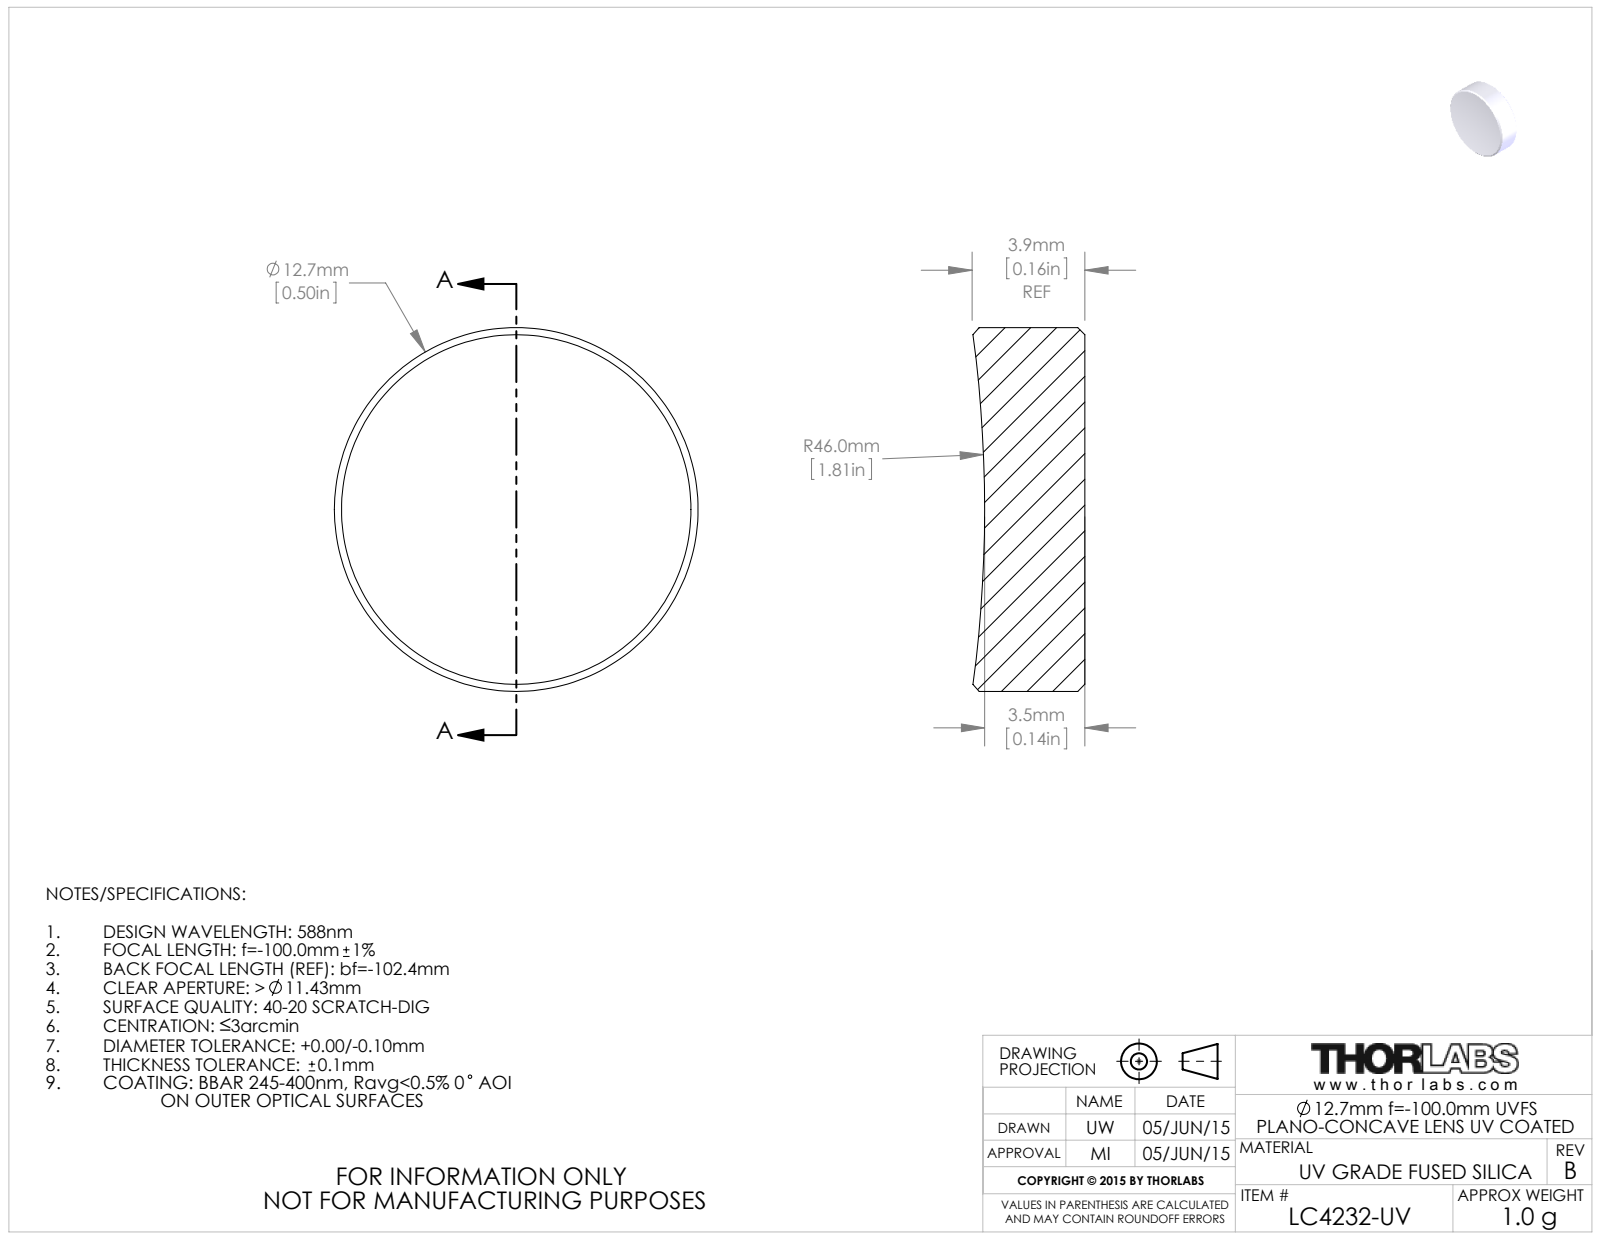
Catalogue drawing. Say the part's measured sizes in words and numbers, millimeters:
The part is named "4348-E0W". Its 3-D file was written by "SolidWorks 2014 (CONFIG_CONTROL_DESIGN)". It is 1 solid with 9 faces: 1 planar, 2 cylindrical and 6 other. Overall it measures 12.7 by 12.7 by 3.91 millimeters. Its volume is 469 cubic millimeters and its surface area 398 square millimeters. Round bosses or shafts: 1 of diameter 12.7.
